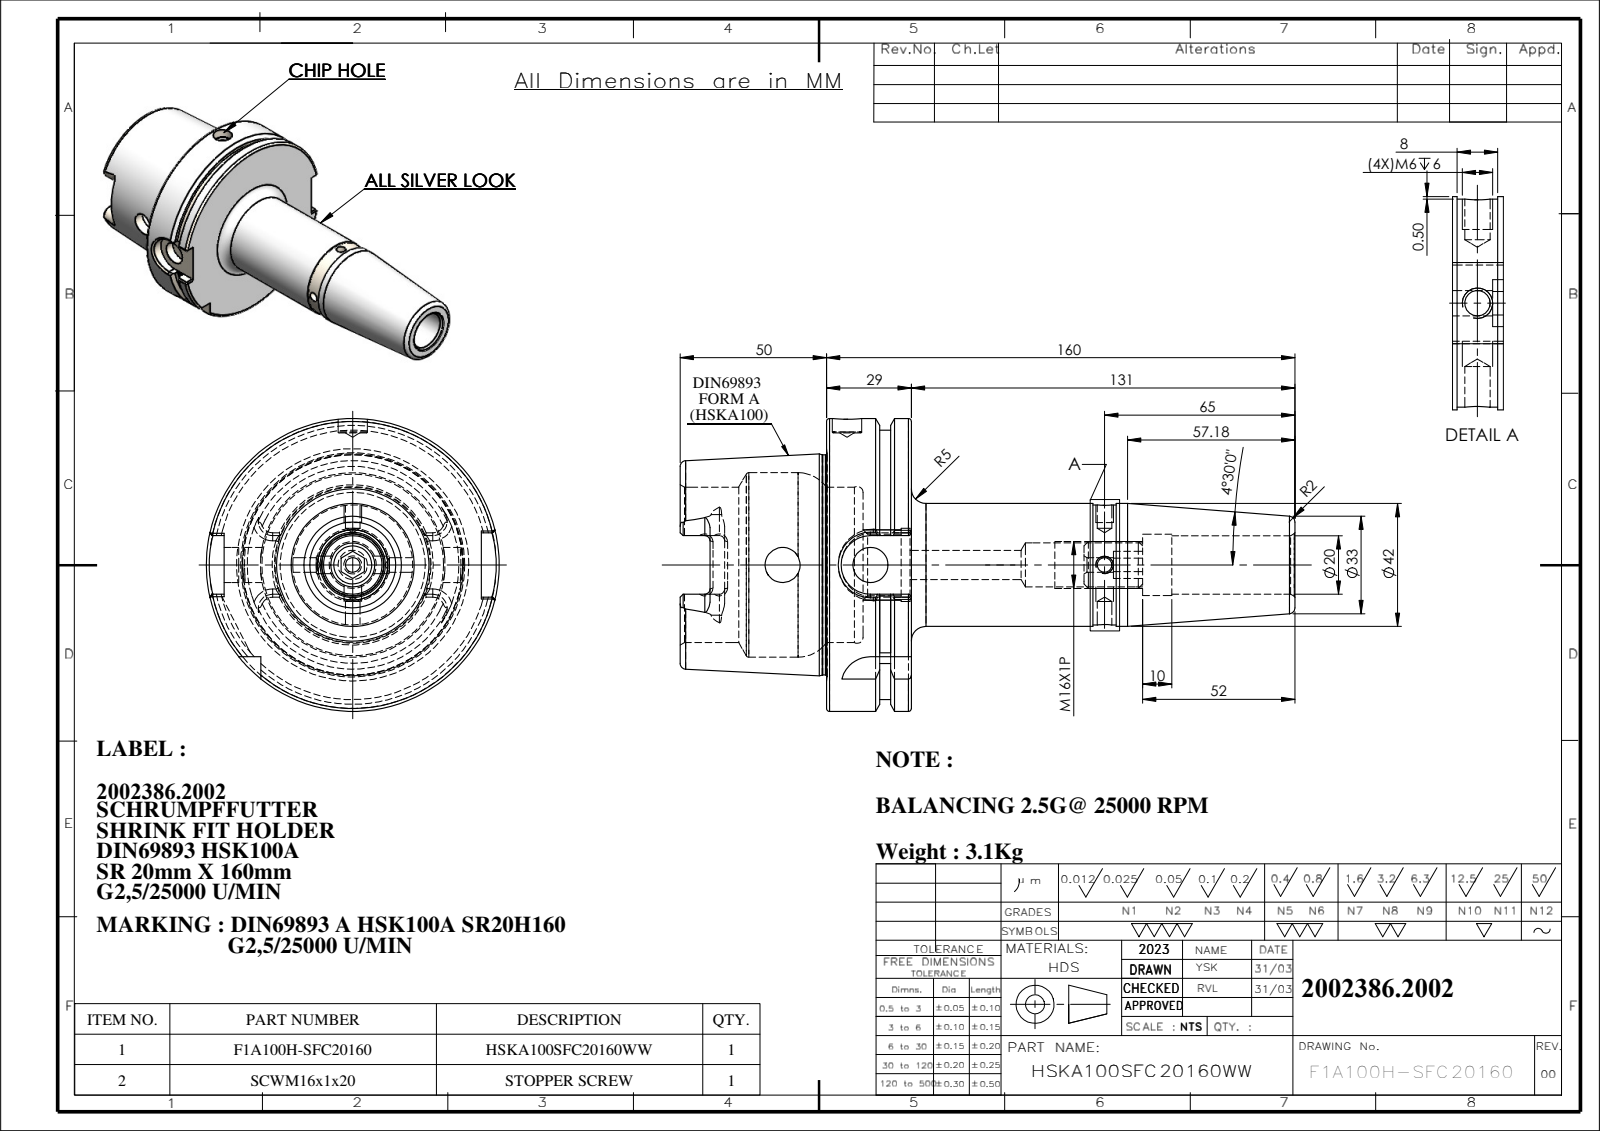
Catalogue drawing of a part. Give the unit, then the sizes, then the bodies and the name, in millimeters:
Units: millimetres
Overall size (bounding box): 209.95 × 100 × 100
Round holes (diameter × count): ⌀5 ×3, ⌀10 ×2, ⌀12 ×2, ⌀15 ×1, ⌀19.98 ×1, ⌀20.98 ×1, ⌀21 ×1, ⌀25 ×1, ⌀53 ×1, ⌀63 ×1
Round bosses / shafts (diameter × count): ⌀100 ×1, ⌀92 ×1, ⌀75.16 ×1, ⌀42 ×1, ⌀41 ×1, ⌀16 ×1
Partial cylindrical surfaces — rounded edges, fillets, slot ends (radius × count): R1.8 ×6, R4.88 ×4, R10 ×2, R11 ×1
Main face-to-face distances: 28.95, 12.5, 16.45, 50, 62.5, 78.95, 78.5, 28.5, 16, 0.45
Hole centre spacings: 30, 79.95, 87.95, 109.95
Volume: 395 139 mm³ · Surface area: 74 087 mm²
Bodies: 2 solids, 222 faces (64 planar, 70 cylindrical, 88 other)
Part name (STEP PRODUCT): SCWM16X1P; 91100A-SR20160; HSKA100SFC20160WW
STEP written by: SolidWorks 2018 (CONFIG_CONTROL_DESIGN)
